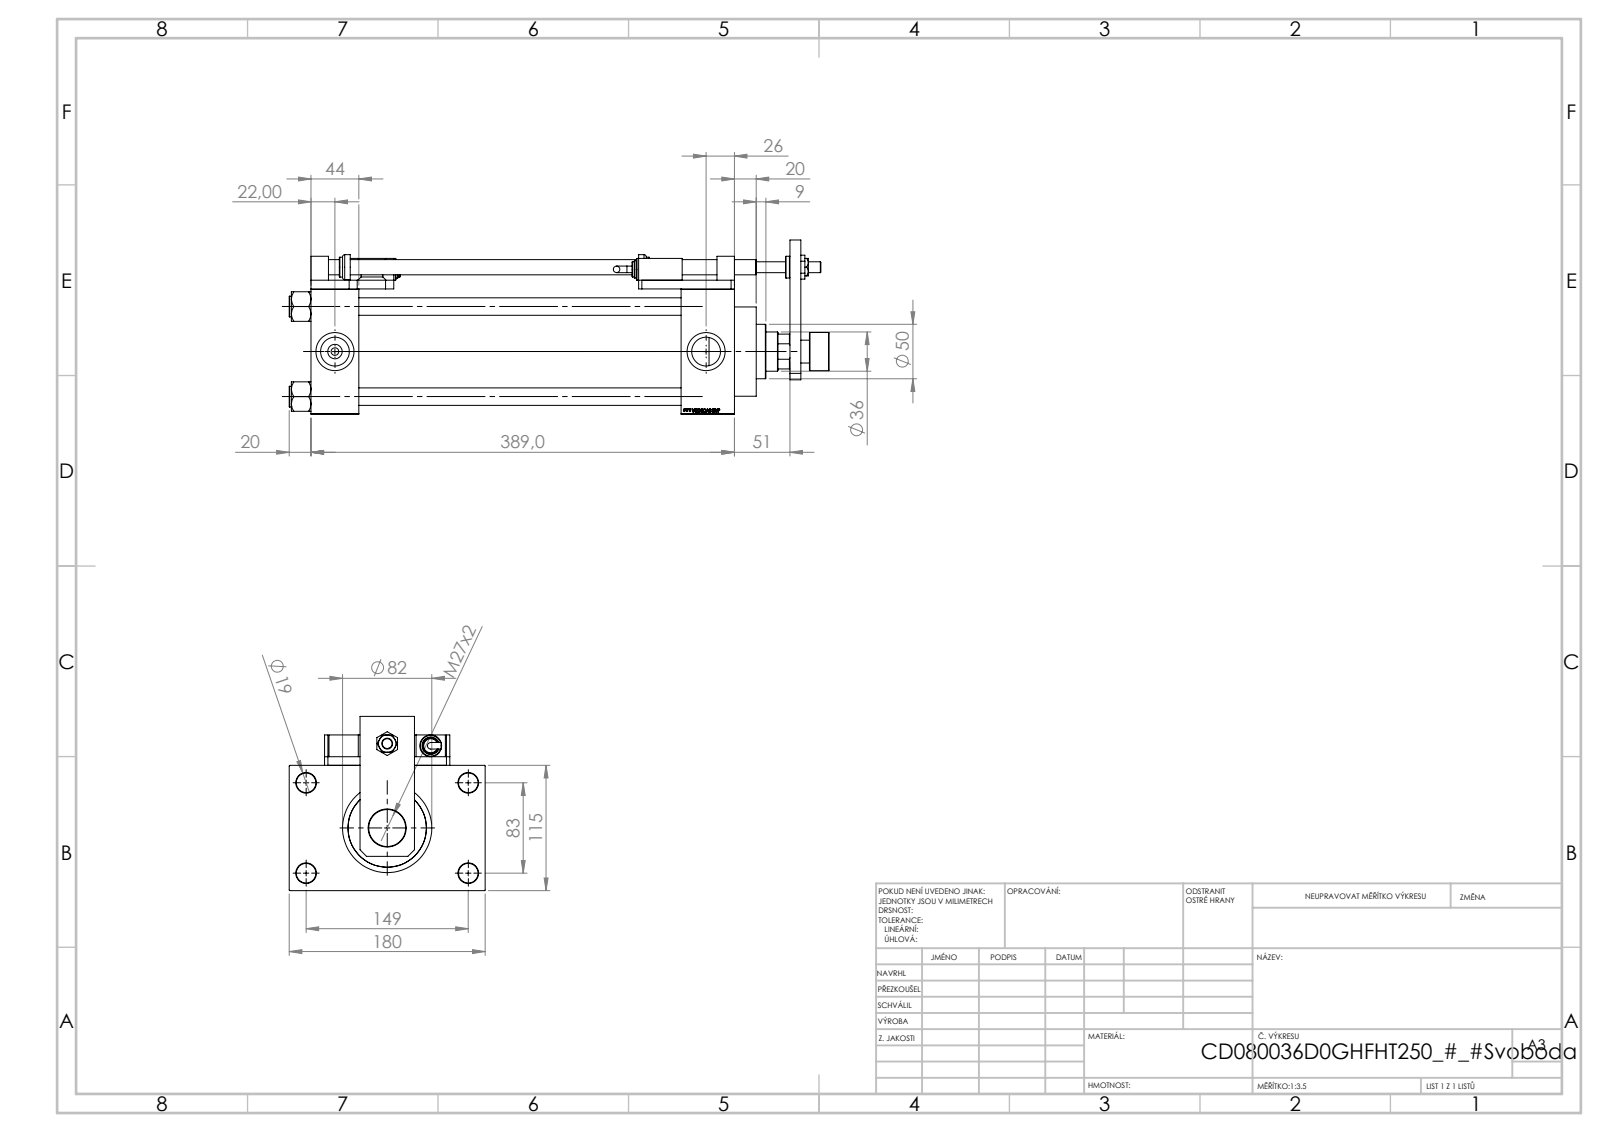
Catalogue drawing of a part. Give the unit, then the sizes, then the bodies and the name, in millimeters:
Units: millimetres
Overall size (bounding box): 496 × 180 × 160
Round holes (diameter × count): ⌀8.5 ×4, ⌀13.5 ×4, ⌀16 ×4, ⌀18 ×4, ⌀7 ×2, ⌀26.44 ×2, ⌀35 ×2, ⌀10 ×1, ⌀14 ×1, ⌀25.5 ×1, ⌀27 ×1, ⌀36 ×1
Round bosses / shafts (diameter × count): ⌀19 ×4, ⌀20 ×3, ⌀16 ×2, ⌀14 ×2, ⌀6 ×2, ⌀86 ×1, ⌀82 ×1, ⌀50 ×1
Partial cylindrical surfaces — rounded edges, fillets, slot ends (radius × count): R7.5 ×4
Main face-to-face distances: 115, 8, 49, 345, 44, 389, 340, 296, 123, 32.5
Hole centre spacings: 33.15, 58.48, 82.7, 85.28, 89.24, 115.85, 142.43, 32
Volume: 2 931 000 mm³ · Surface area: 595 707 mm²
Bodies: 25 solids, 1393 faces (670 planar, 160 cylindrical, 563 other)
Part name (STEP PRODUCT): V215CD_D_Body; V215CD_SWITCH_Q_ZARAZKA; V215CD_SWITCH_Q_NUT; V215CD_VC_A (+7 more)
STEP written by: SolidWorks 2019 (CONFIG_CONTROL_DESIGN)
